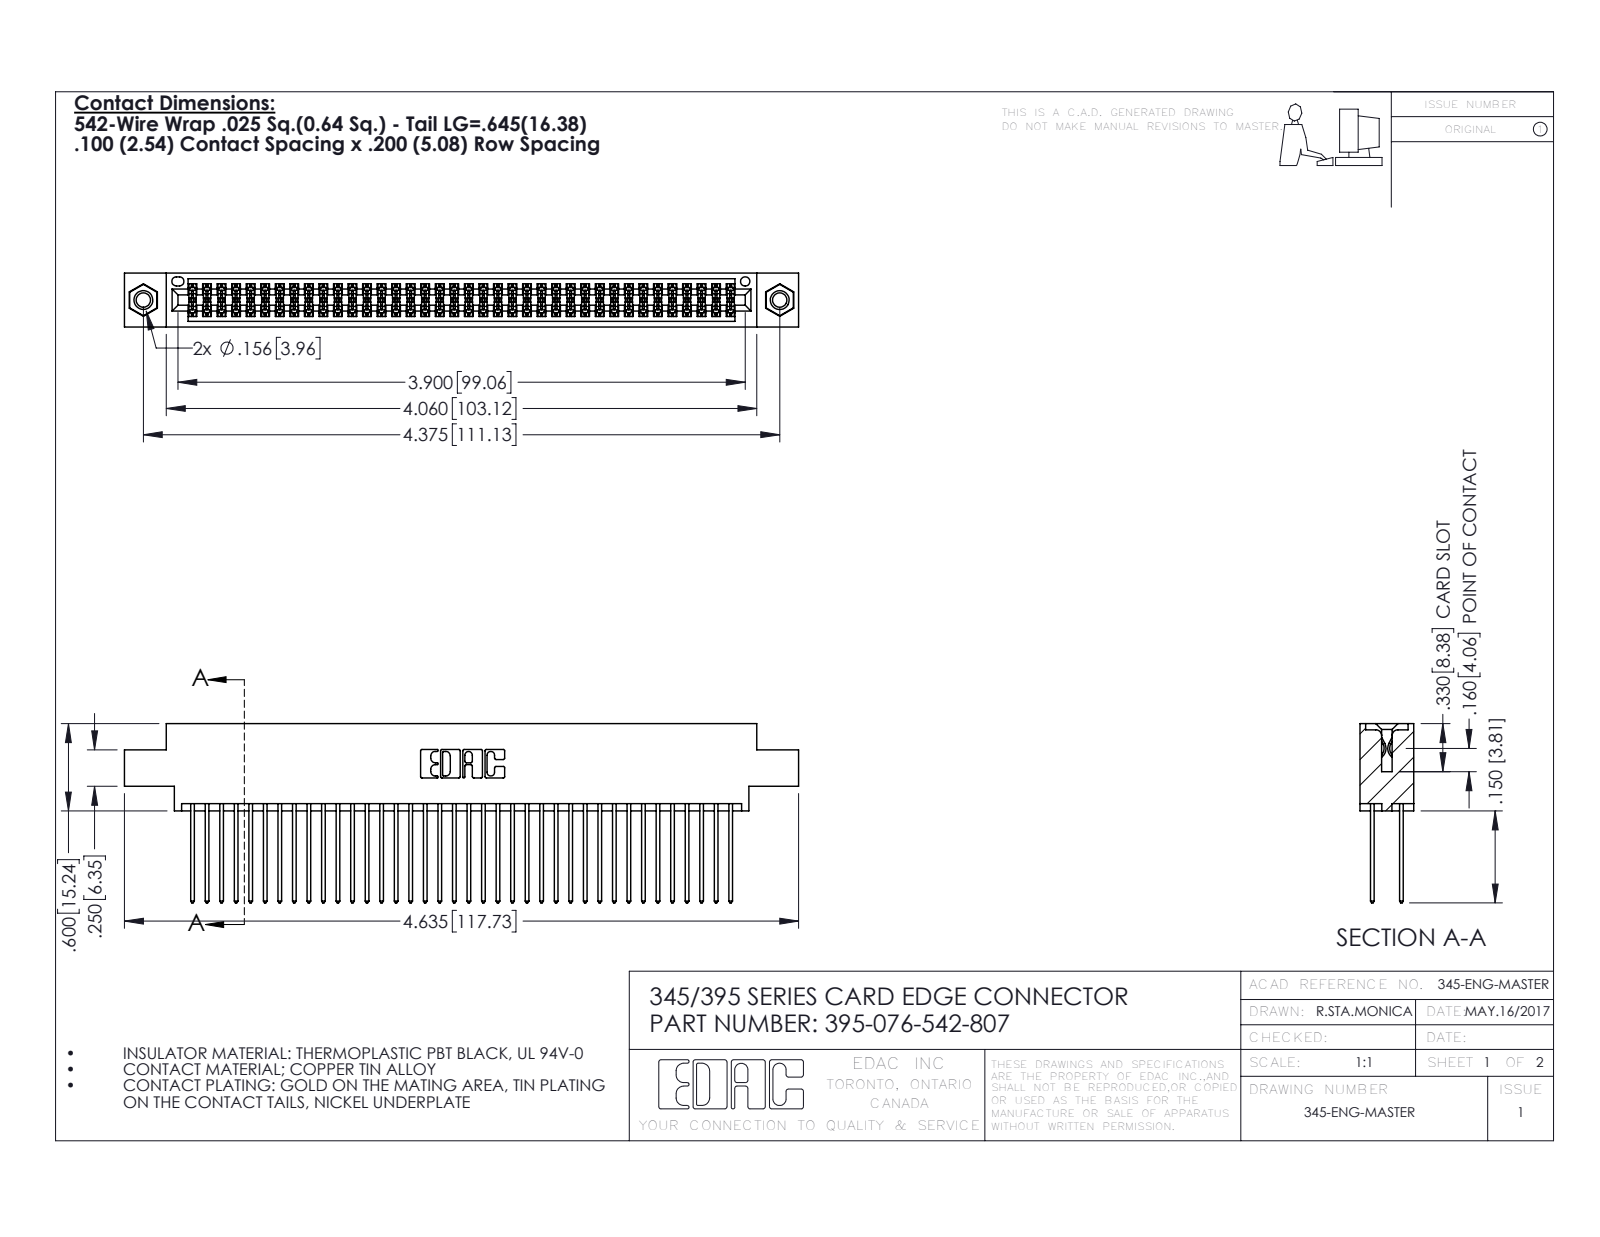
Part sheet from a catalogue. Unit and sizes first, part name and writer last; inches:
Units: inches
Overall size (bounding box): 4.635 × 1.232 × 0.37
Round holes (diameter × count): ⌀0.098 ×2, ⌀0.125 ×2, ⌀0.156 ×2, ⌀0.064 ×1
Round bosses / shafts (diameter × count): ⌀0.155 ×2
Partial cylindrical surfaces — rounded edges, fillets, slot ends (radius × count): R0.006 ×114, R0.01 ×76, R0.01 ×22, R0.007 ×6, R0.031 ×6, R0.026 ×3, R0.014 ×2, R0.019 ×2
Main face-to-face distances: 0.072, 0.298, 0.2, 0.098, 0.272, 0.025, 0.37, 0.225, 0.175, 0.149
Hole centre spacings: 0.27, 4.139, 4.375
Volume: 0.709 in³ · Surface area: 29.35 in²
Bodies: 79 solids, 3990 faces (2624 planar, 1350 cylindrical, 16 other)
Part name (STEP PRODUCT): 395-076-542-807; 345-292-001_345-293-142; 345-250-001_345-250-005-103; 345 Part_0.170 Offset - 0.156 Dia-TI
STEP written by: SolidWorks 2016 (CONFIG_CONTROL_DESIGN)
